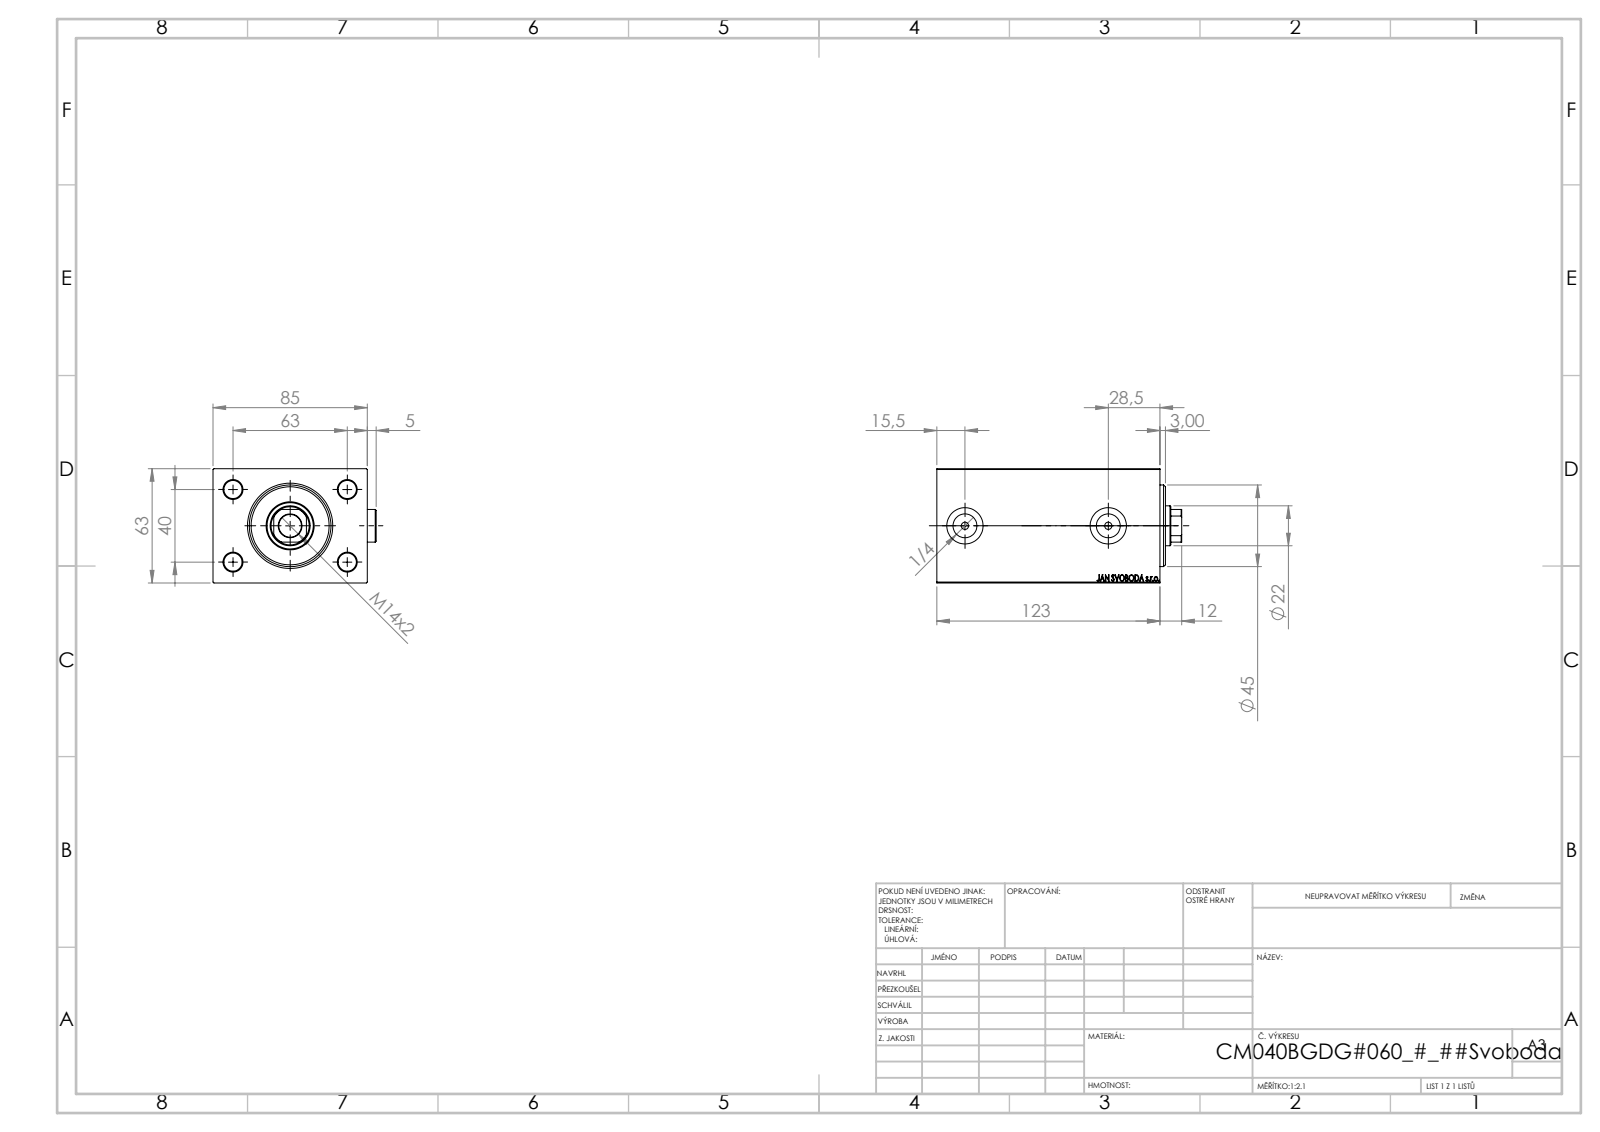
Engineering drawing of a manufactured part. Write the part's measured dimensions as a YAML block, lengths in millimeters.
part_name: "V450CM_B_Body; Zatka_OIL_PORT; V450CM_VC_B; V450CM_B_VCP"
step_written_by: "SolidWorks 2019 (CONFIG_CONTROL_DESIGN)"
units: millimeters
bodies: {solids: 5, faces: 935, planar: 435, cylindrical: 70, other: 430}
overall_size: [135, 89.9, 63]
volume: 592286
surface_area: 89758
round_holes:
  - {diameter: 10, count: 4}
  - {diameter: 4, count: 2}
  - {diameter: 13.16, count: 2}
  - {diameter: 20, count: 2}
  - {diameter: 12.5, count: 1}
  - {diameter: 22, count: 1}
  - {diameter: 25.5, count: 1}
  - {diameter: 26.5, count: 1}
  - {diameter: 40, count: 1}
  - {diameter: 42, count: 1}
  - {diameter: 45, count: 1}
round_bosses_or_shafts:
  - {diameter: 18, count: 2}
partial_cylinders:
  - {radius: 10.5, count: 1}
face_to_face_distances: [63, 85, 12, 111, 123, 84.9, 99, 72, 3, 15]
hole_center_spacings: [37.31, 40, 63, 74.63, 79]
